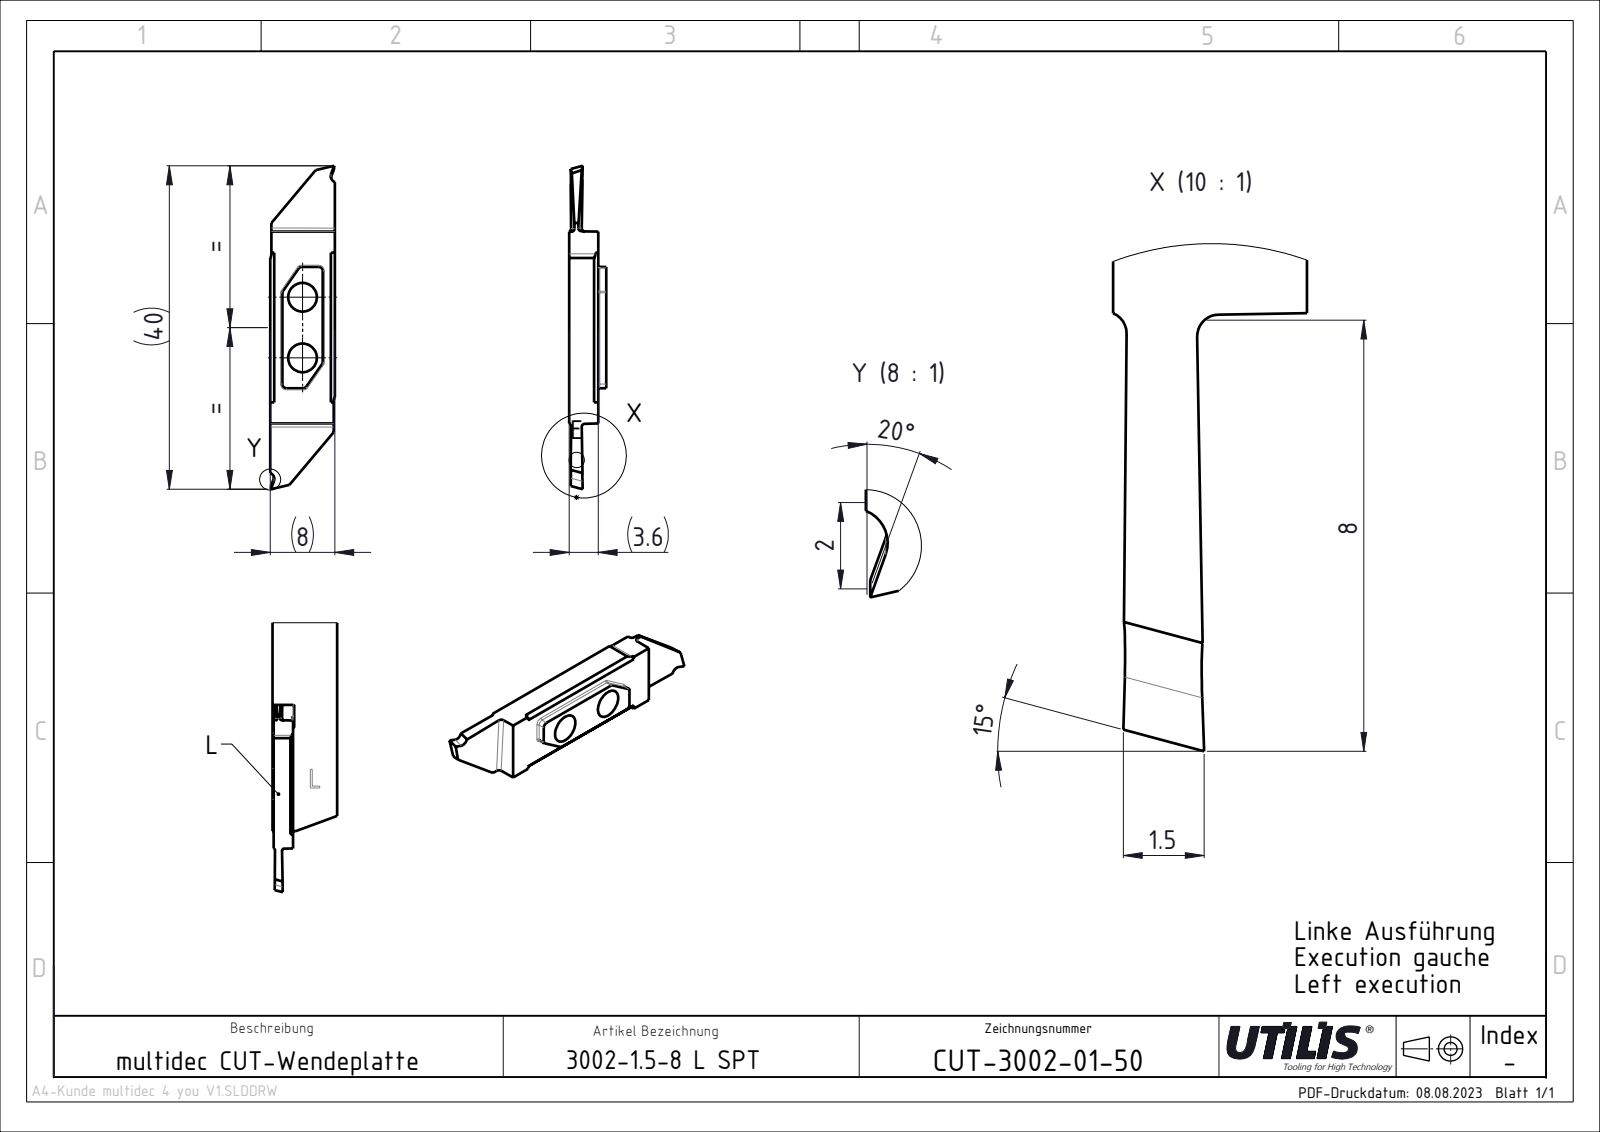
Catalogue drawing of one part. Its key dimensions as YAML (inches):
part_name: "CUT-3002 SPT; ASME Y14.5"
step_written_by: "SolidWorks 2023 SP4 || FormatWorks Professional (AP242_MANAGED_MODEL_BASED_3D_ENGINEERING_MIM_LF)"
units: inches
bodies: {solids: 1, faces: 32, planar: 22, cylindrical: 10, other: 0}
overall_size: [1.575, 0.315, 0.142]
volume: 0.044
surface_area: 1.3
round_holes:
  - {diameter: 0.14, count: 2}
partial_cylinders:
  - {radius: 0.016, count: 4}
  - {radius: 0.039, count: 2}
face_to_face_distances: [0.142, 0.315, 0.309, 0.887, 0.303, 0.728]
hole_center_spacings: [0.295]
